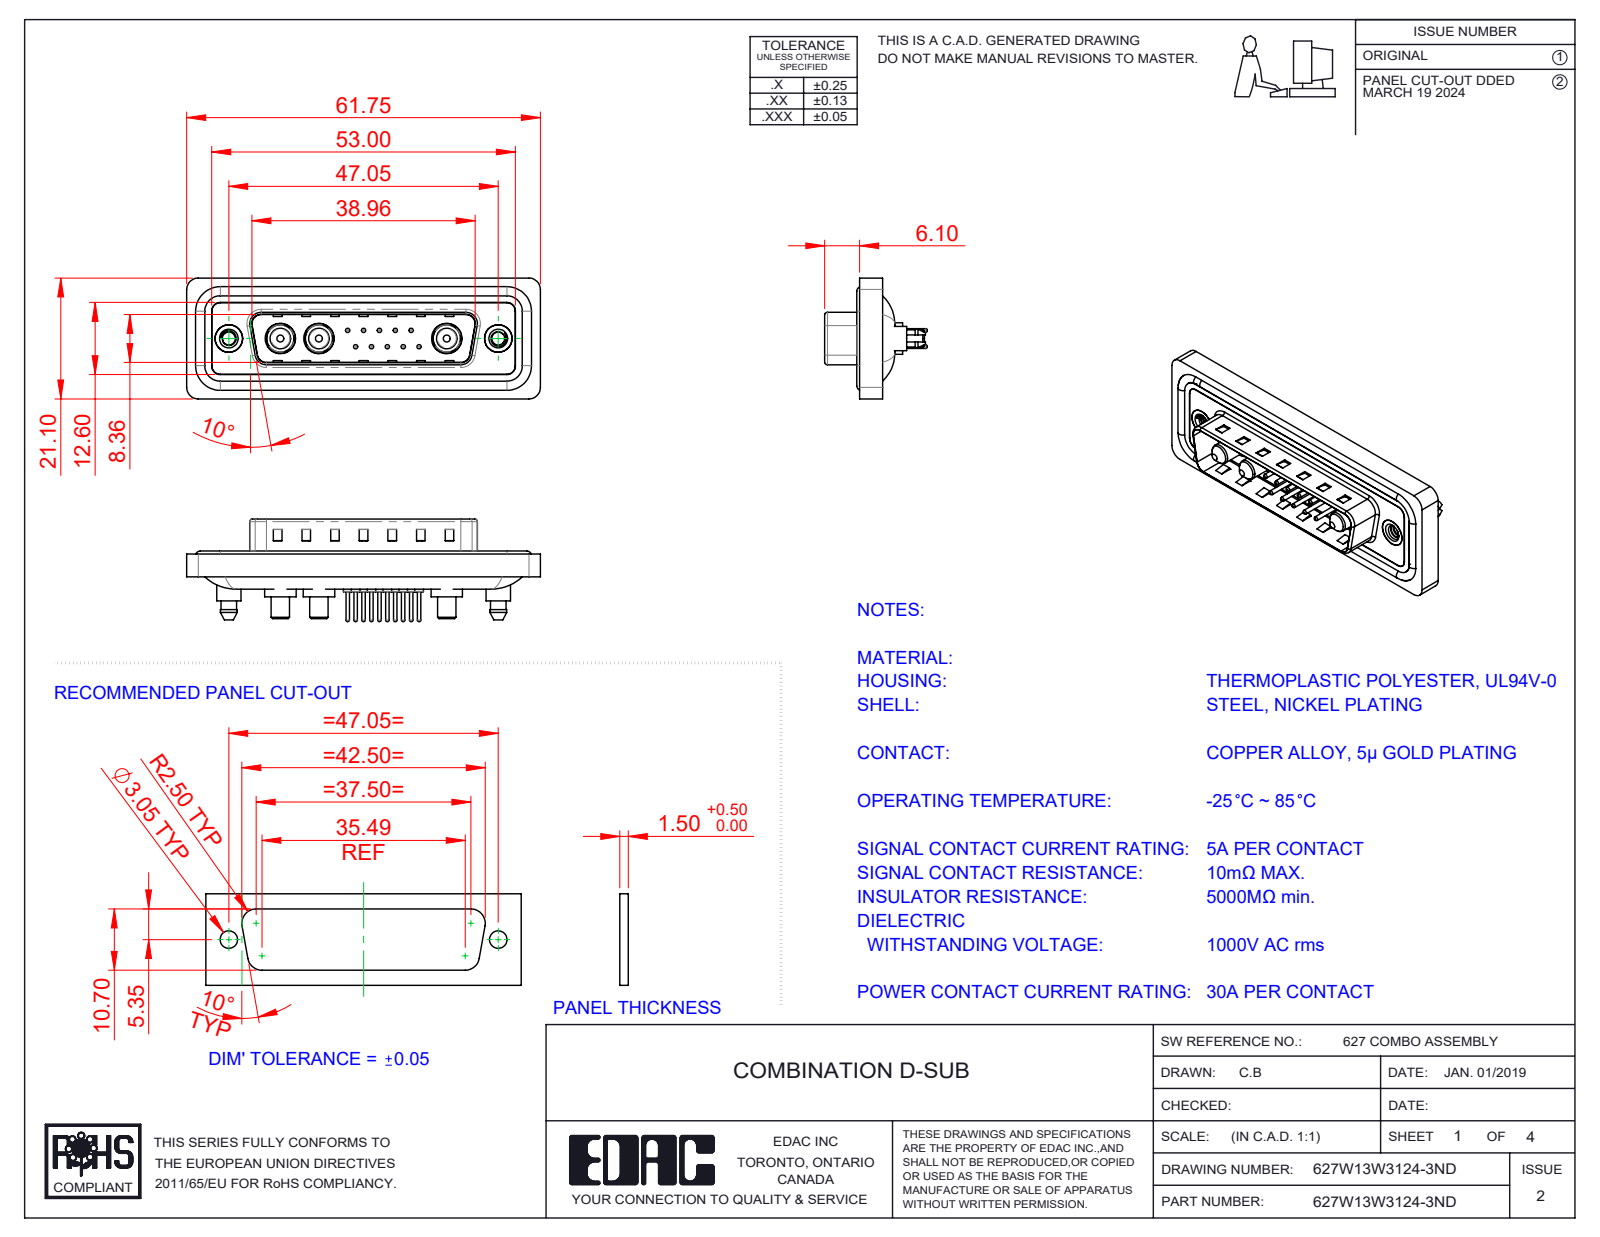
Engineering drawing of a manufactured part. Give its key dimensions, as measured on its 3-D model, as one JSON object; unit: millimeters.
{"part_name": "627Combo Waterproof Housing_25 Contacts; 627Combo Shell Front_25 Contacts; 627Combo Contact Row 2_24; 627Combo Contact Row 1_24 (+6 more)", "step_written_by": "SolidWorks 2023 (CONFIG_CONTROL_DESIGN)", "units": "millimeters", "bodies": {"solids": 23, "faces": 1028, "planar": 325, "cylindrical": 425, "other": 278}, "overall_size": [61.75, 21.1, 17.9], "volume_mm3": 7491, "surface_area_mm2": 12225, "round_holes": [[0.75, 10], [1.6, 10], [2, 10], [4.85, 3], [5.3, 3], [2.26, 2], [4, 2], [4.8, 2], [5, 2]], "round_bosses_or_shafts": [[1.5, 10], [0.6, 10], [1.6, 4], [5.5, 3], [5.2, 3], [4.75, 3], [3.75, 3], [3.6, 3]], "partial_cylinders_radius": [[1.5, 24], [2, 18], [1.6, 10], [0.5, 8], [0.25, 4], [0.6, 4], [0.65, 4], [0.9, 4]], "face_to_face_distances": [0.4, 1.5, 1.1, 1.6, 0.5, 3.1, 2.9, 0.82, 9.58, 4.1], "hole_center_spacings": [3.16, 2.77, 5.04, 5.54, 7.49, 5.03, 8.31, 10.11]}
